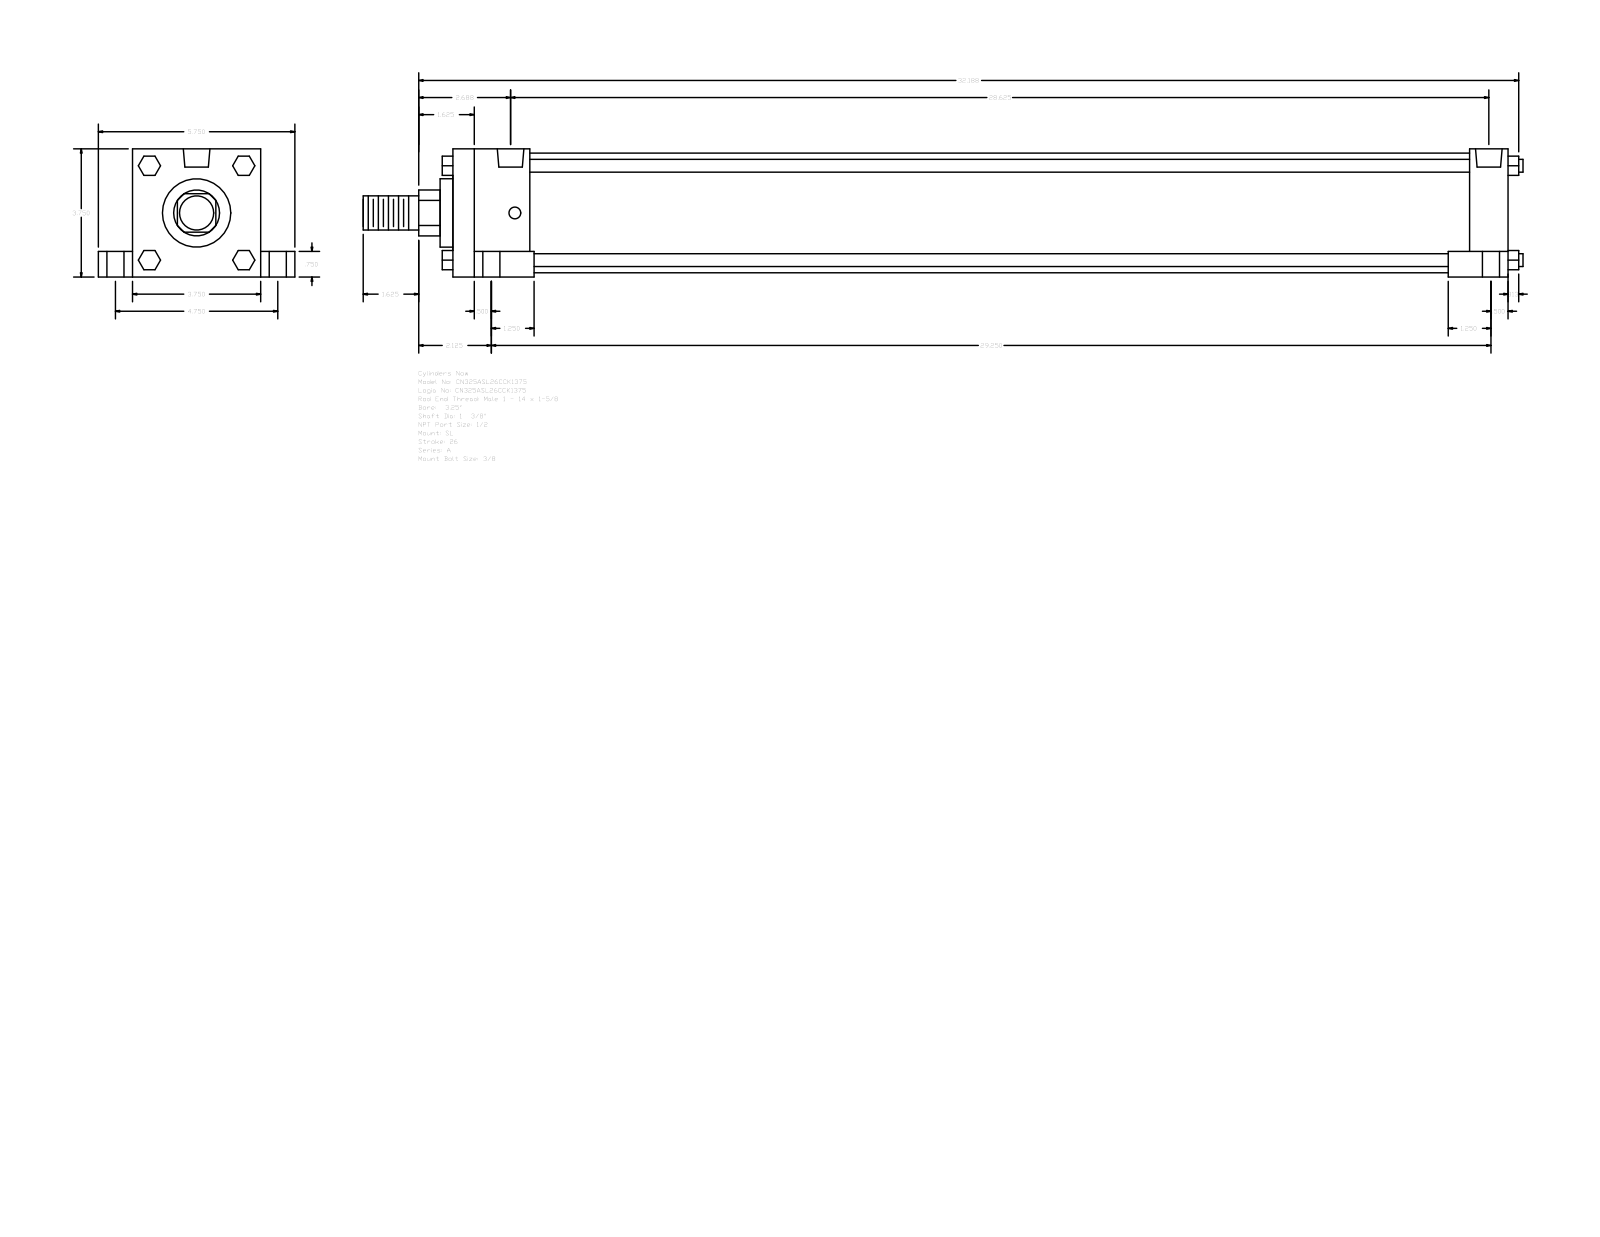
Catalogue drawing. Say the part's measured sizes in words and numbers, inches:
The part is named "A_SL__0325_1.375". Its 3-D file was written by "GSSL Pune (CONFIG_CONTROL_DESIGN)". It is 0 solids with 150 faces: 114 planar, 36 cylindrical and 0 other. Overall it measures 33.937 by 5.75 by 3.75 inches. Round holes: 4 of diameter 0.344, 4 of diameter 0.5, 4 of diameter 0.75, 2 of diameter 0.778. Round bosses or shafts: 4 of diameter 0.375, 1 of diameter 3.5, 1 of diameter 2, 1 of diameter 1.375, 1 of diameter 1. Partial cylindrical surfaces (rounded edges, fillets, slot ends): 1 of radius 0.672. The main face-to-face distances are 3.75, 30.875, 1, 4.75, 0.75, 3, 2.25, 1.125, 29.75, 27.5. The hole center spacings are 0.125, 2.376, 2.383, 2.441, 2.473, 4.75, 28.375, 28.5.
